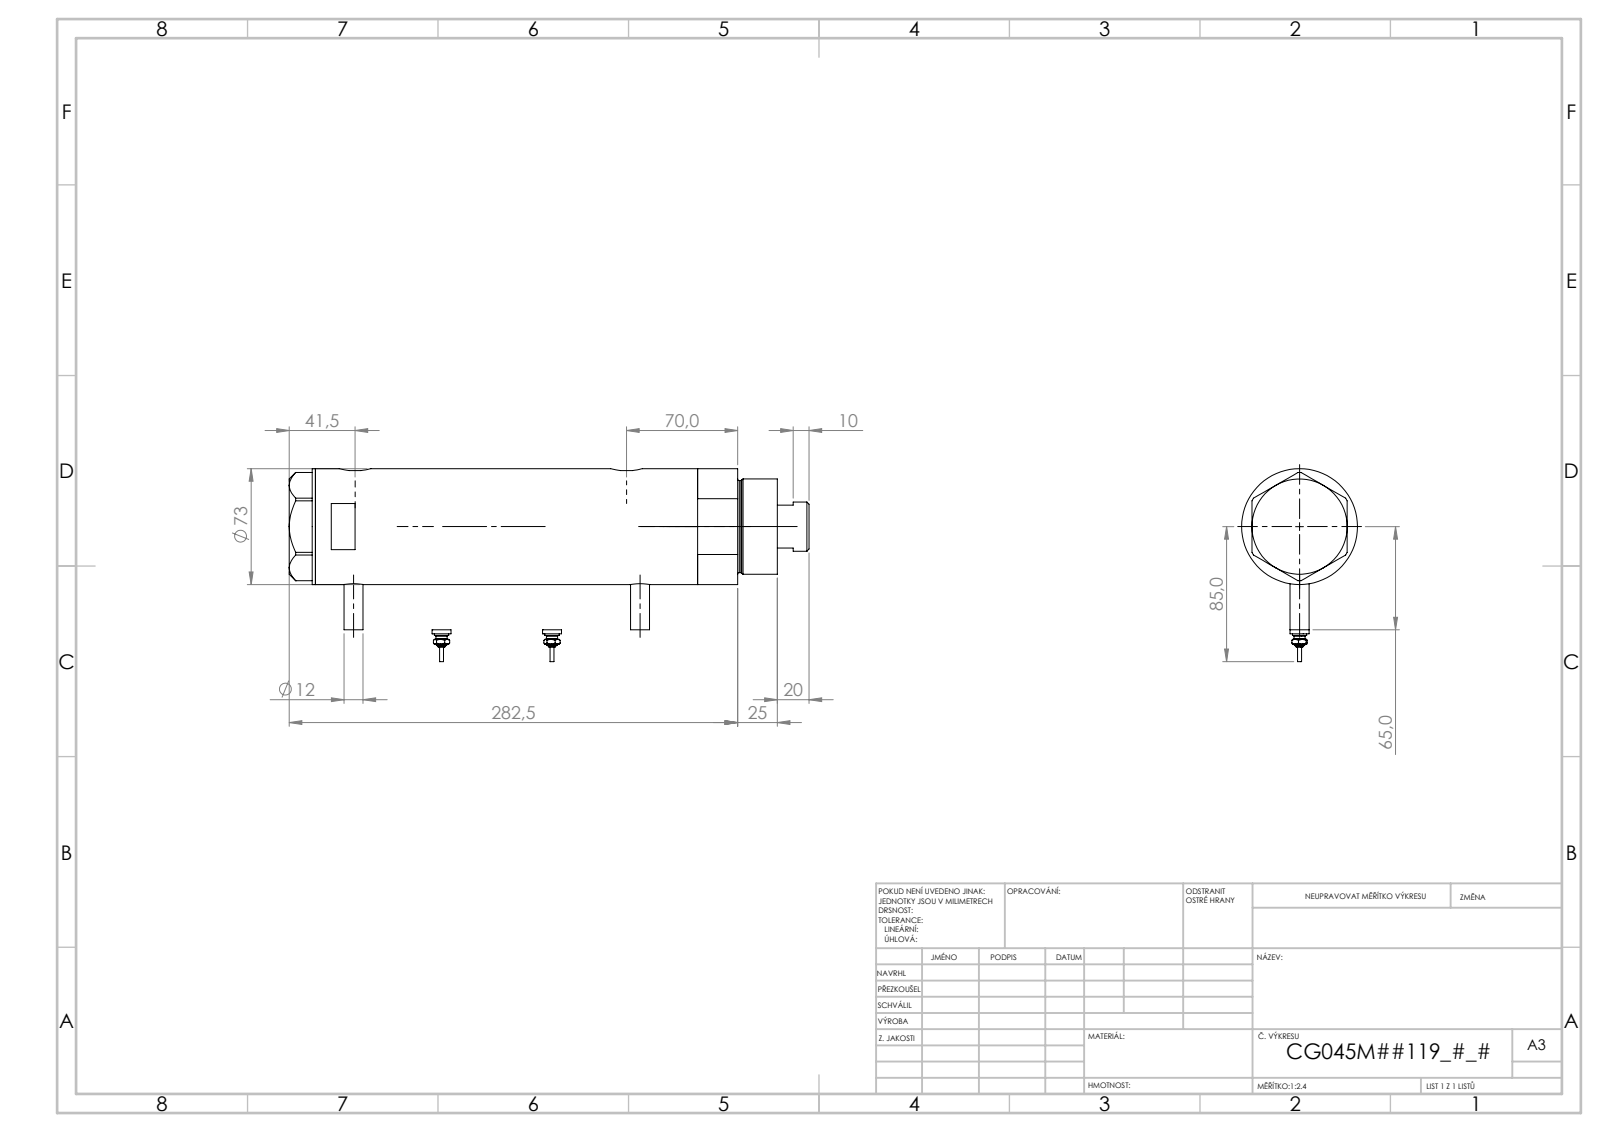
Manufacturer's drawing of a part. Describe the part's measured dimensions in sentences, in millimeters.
The part is named "Switch; V270CG_VC; V270CG_BACK; V270CG_FRONT (+1 more)". Its 3-D file was written by "SolidWorks 2019 (CONFIG_CONTROL_DESIGN)". It is 6 solids with 212 faces: 77 planar, 71 cylindrical and 64 other. Overall it measures 327.5 by 121.5 by 73 millimeters. Its volume is 1 152 000 cubic millimeters and its surface area 187 317 square millimeters. Round holes: 2 of diameter 12.5, 2 of diameter 13.16, 1 of diameter 10.5, 1 of diameter 32, 1 of diameter 33.5, 1 of diameter 45, 1 of diameter 48, 1 of diameter 64. Round bosses or shafts: 4 of diameter 12, 2 of diameter 9, 2 of diameter 7, 2 of diameter 4.5, 2 of diameter 2.5, 1 of diameter 73, 1 of diameter 60, 1 of diameter 58. Partial cylindrical surfaces (rounded edges, fillets, slot ends): 2 of radius 10. The main face-to-face distances are 196, 26, 170, 16.5, 42.5, 212.5, 2, 291, 307.5, 265. The hole center spacings are 1, 8.5, 171, 172, 179.5, 180.5.
